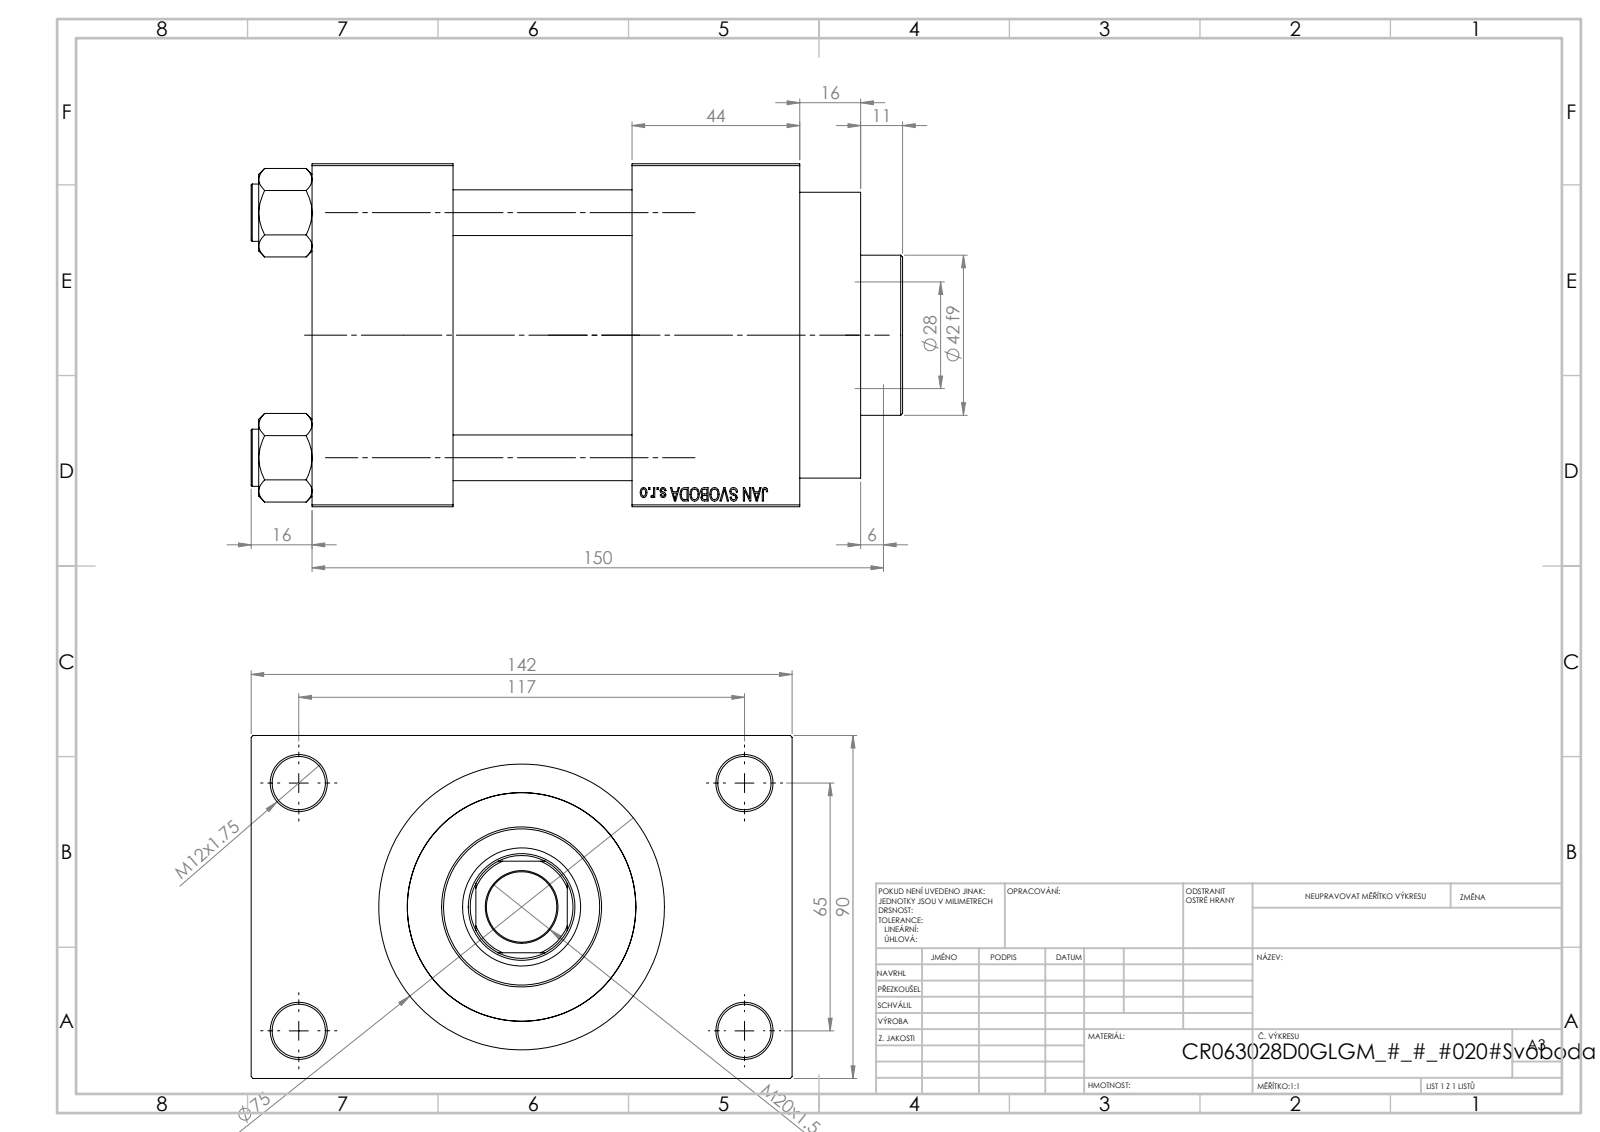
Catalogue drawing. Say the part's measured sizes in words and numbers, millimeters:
The part is named "NUT_M5_D; V215CR_D_Body; V215_VC_A; V215CR_VCP_D (+1 more)". Its 3-D file was written by "SolidWorks 2019 (CONFIG_CONTROL_DESIGN)". It is 11 solids with 1104 faces: 497 planar, 89 cylindrical and 518 other. Overall it measures 171 by 142 by 90 millimeters. Its volume is 1 030 000 cubic millimeters and its surface area 184 679 square millimeters. Round holes: 4 of diameter 12, 4 of diameter 14, 2 of diameter 7, 2 of diameter 20.96, 2 of diameter 30, 1 of diameter 18.5, 1 of diameter 28, 1 of diameter 31, 1 of diameter 50, 1 of diameter 60, 1 of diameter 63. Round bosses or shafts: 4 of diameter 15, 1 of diameter 75, 1 of diameter 69, 1 of diameter 42. Partial cylindrical surfaces (rounded edges, fillets, slot ends): 1 of radius 13.5. The main face-to-face distances are 90, 47, 37, 84, 91, 128, 44, 26, 116, 64. The hole center spacings are 26.35, 45.47, 64.3, 66.92, 69.81, 90.65, 111.34, 65.
